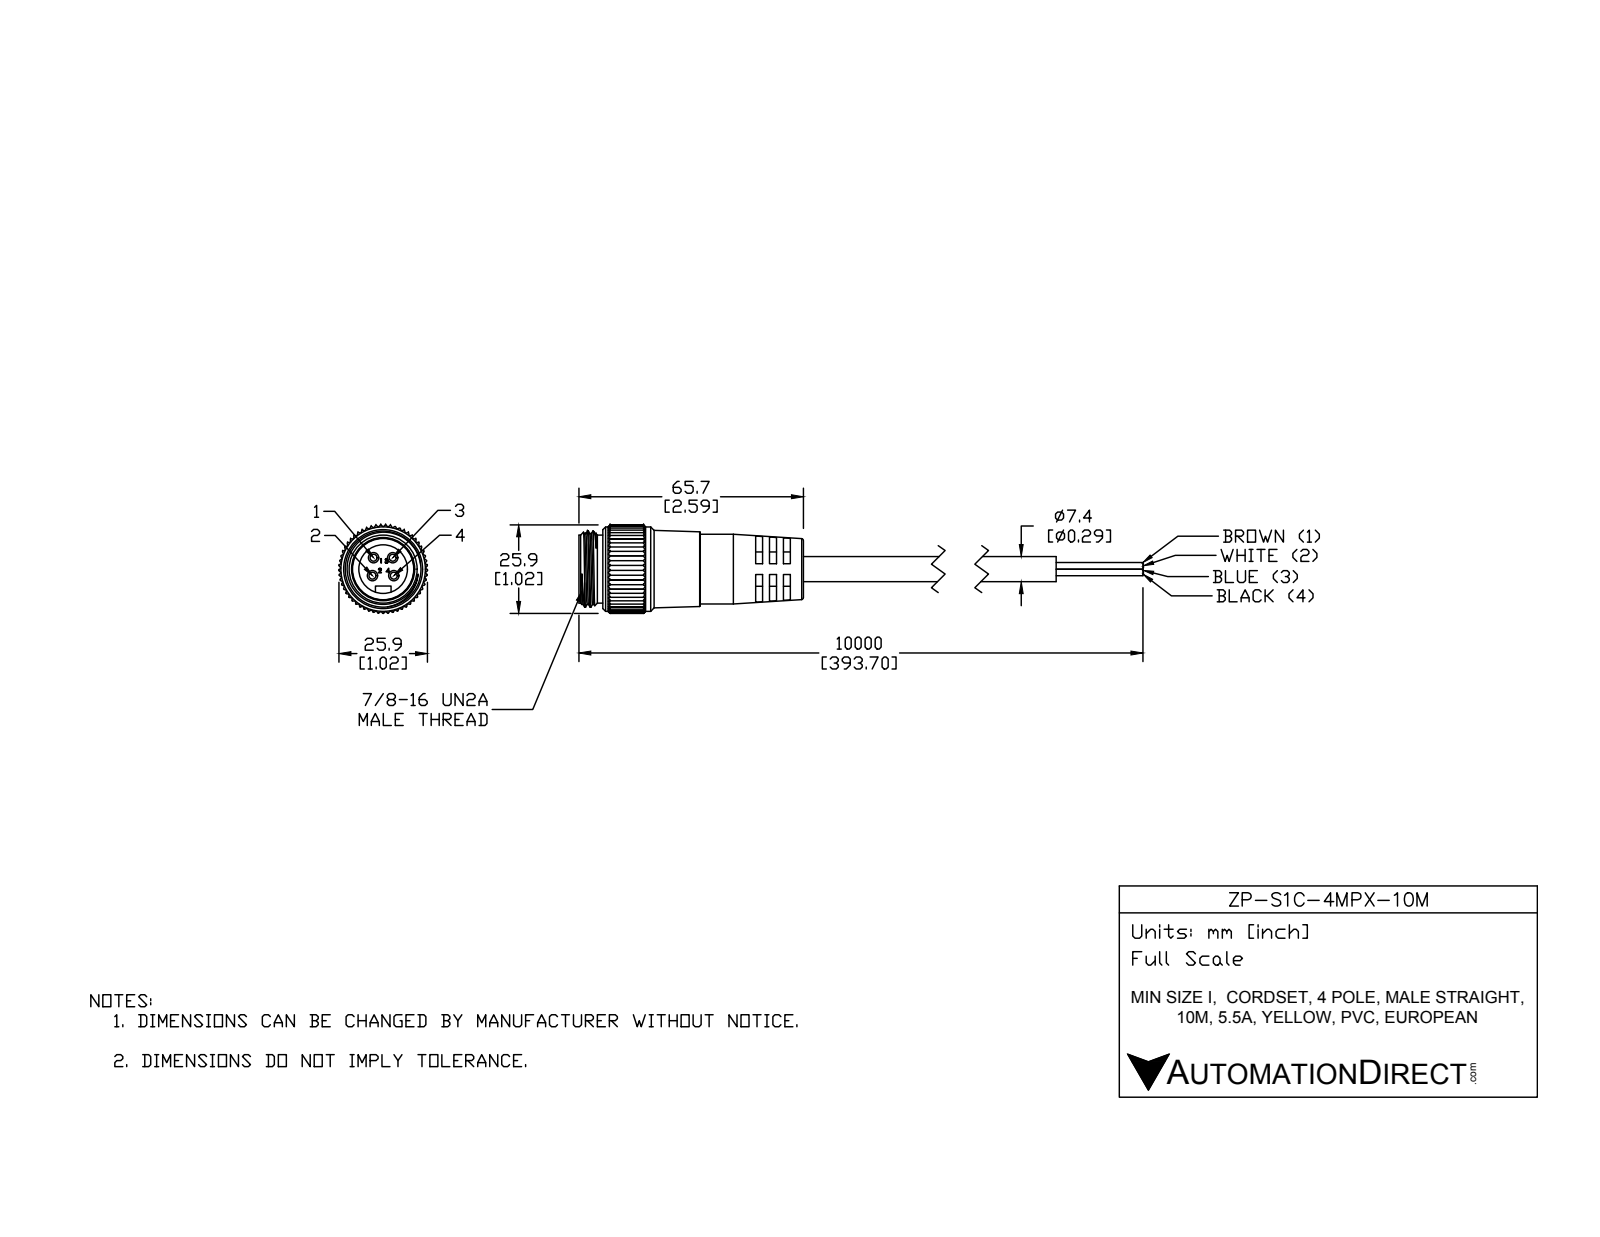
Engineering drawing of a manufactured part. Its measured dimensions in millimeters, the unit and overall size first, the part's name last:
Units: millimetres
Overall size (bounding box): 115.9 × 25.84 × 25.83
Round holes (diameter × count): ⌀14.22 ×1, ⌀17.88 ×1, ⌀19.96 ×1, ⌀20.45 ×1, ⌀21 ×1
Round bosses / shafts (diameter × count): ⌀3.05 ×4, ⌀2 ×4, ⌀24.68 ×1, ⌀22.22 ×1, ⌀20.4 ×1, ⌀19.5 ×1, ⌀9.91 ×1
Partial cylindrical surfaces — rounded edges, fillets, slot ends (radius × count): R0.25 ×165, R2.29 ×1, R5.25 ×1, R12.93 ×1
Main face-to-face distances: 2, 4.04, 13.88, 11.88, 2.04, 9.84, 6.04, 7.84, 2.02, 8.06
Volume: 26 095 mm³ · Surface area: 13 335 mm²
Bodies: 6 solids, 606 faces (218 planar, 326 cylindrical, 62 other)
Part name (STEP PRODUCT): ZP-S1C-4MPX-10M
STEP written by: SolidWorks 2015 (AUTOMOTIVE_DESIGN)
